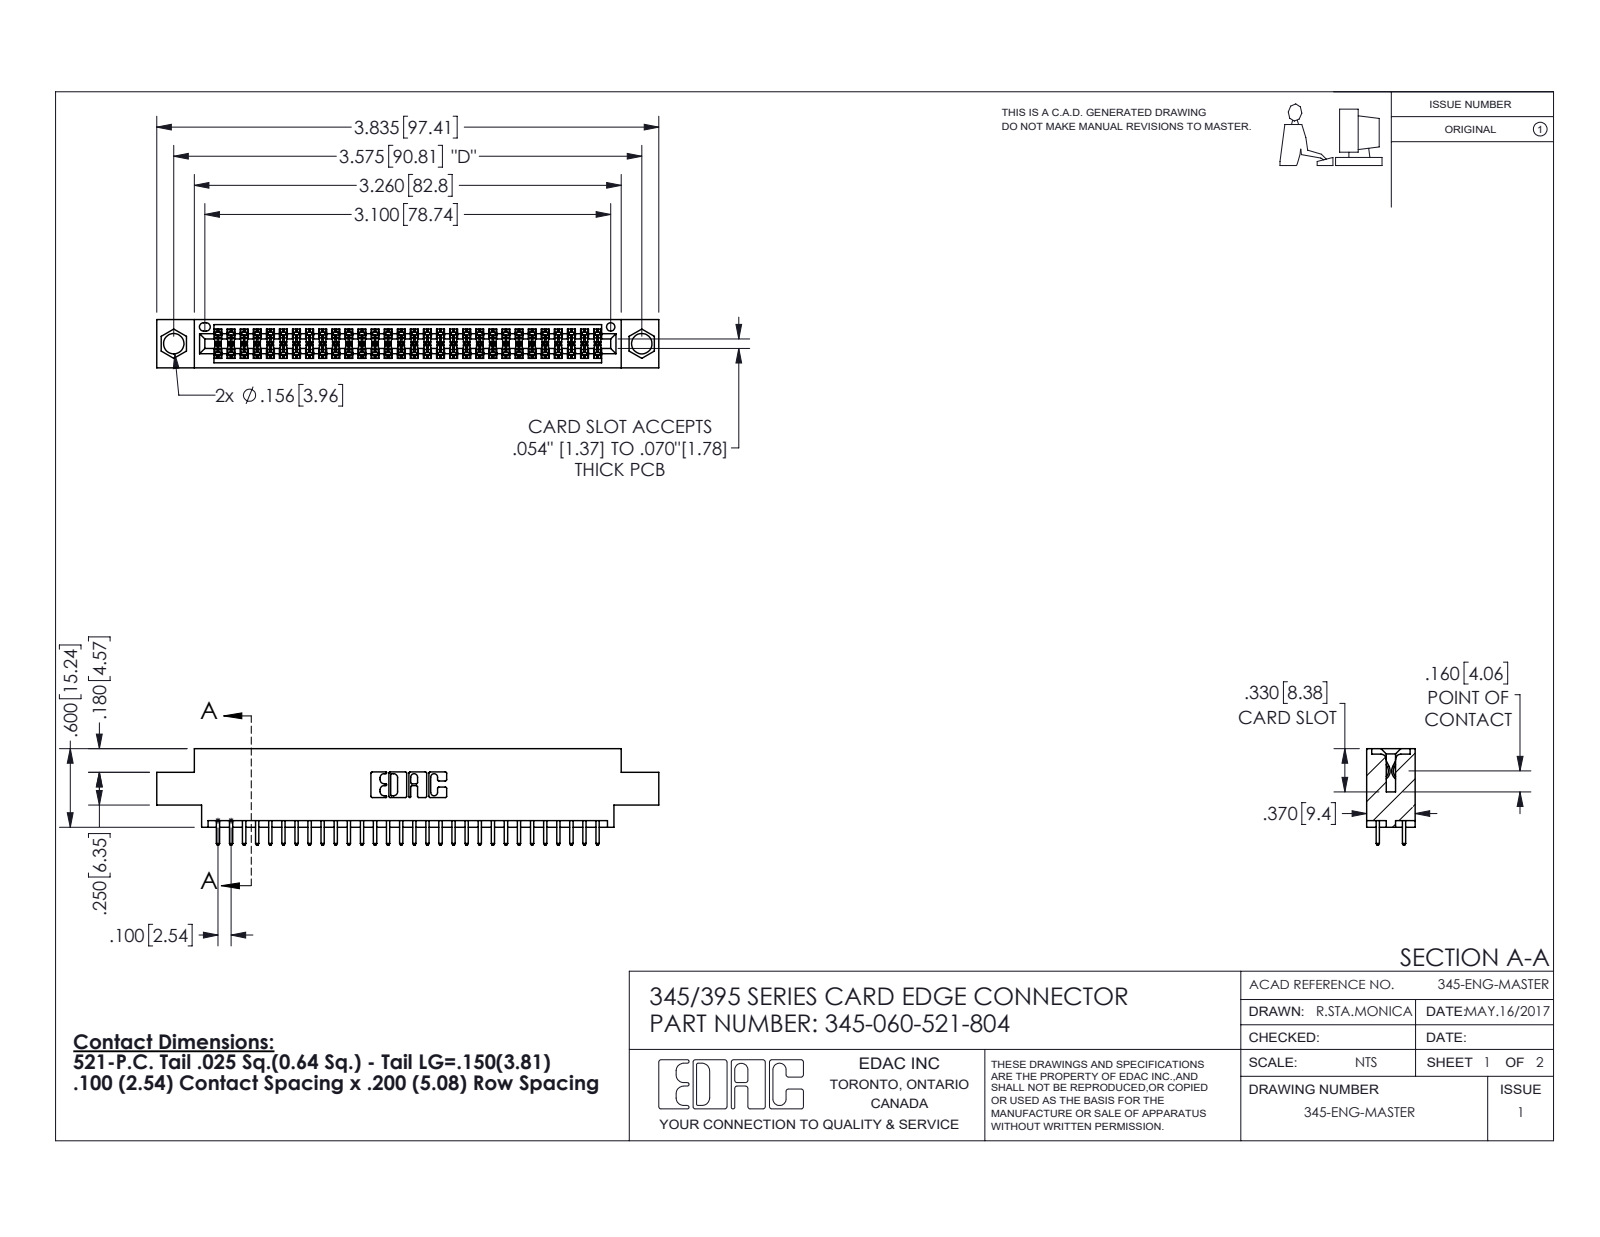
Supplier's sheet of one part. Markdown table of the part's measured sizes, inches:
| quantity | value |
| --- | --- |
| part name | 345-060-521-804; 345-292-001_345-293-121; 345 Part_0.170 Offset - 0.156 Dia-TI |
| STEP written by | SolidWorks 2020 (CONFIG_CONTROL_DESIGN) |
| units | inches |
| bodies | 61 solids, 3144 faces (2078 planar, 1066 cylindrical, 0 other) |
| overall size | 3.835 × 0.737 × 0.37 |
| volume | 0.556 in³ |
| surface area | 20.25 in² |
| round holes (diameter × count) | 0.156 × 2, 0.064 × 1 |
| partial cylindrical surfaces (radius × count) | 0.006 × 120, 0.01 × 60, 0.01 × 22, 0.007 × 6, 0.031 × 6, 0.026 × 3, 0.014 × 2, 0.019 × 2 |
| main face-to-face distances | 0.072, 0.298, 0.37, 0.2, 0.098, 0.272, 0.025, 0.225, 0.175, 0.149 |
| hole center spacings | 0.27, 3.34, 3.575 |
